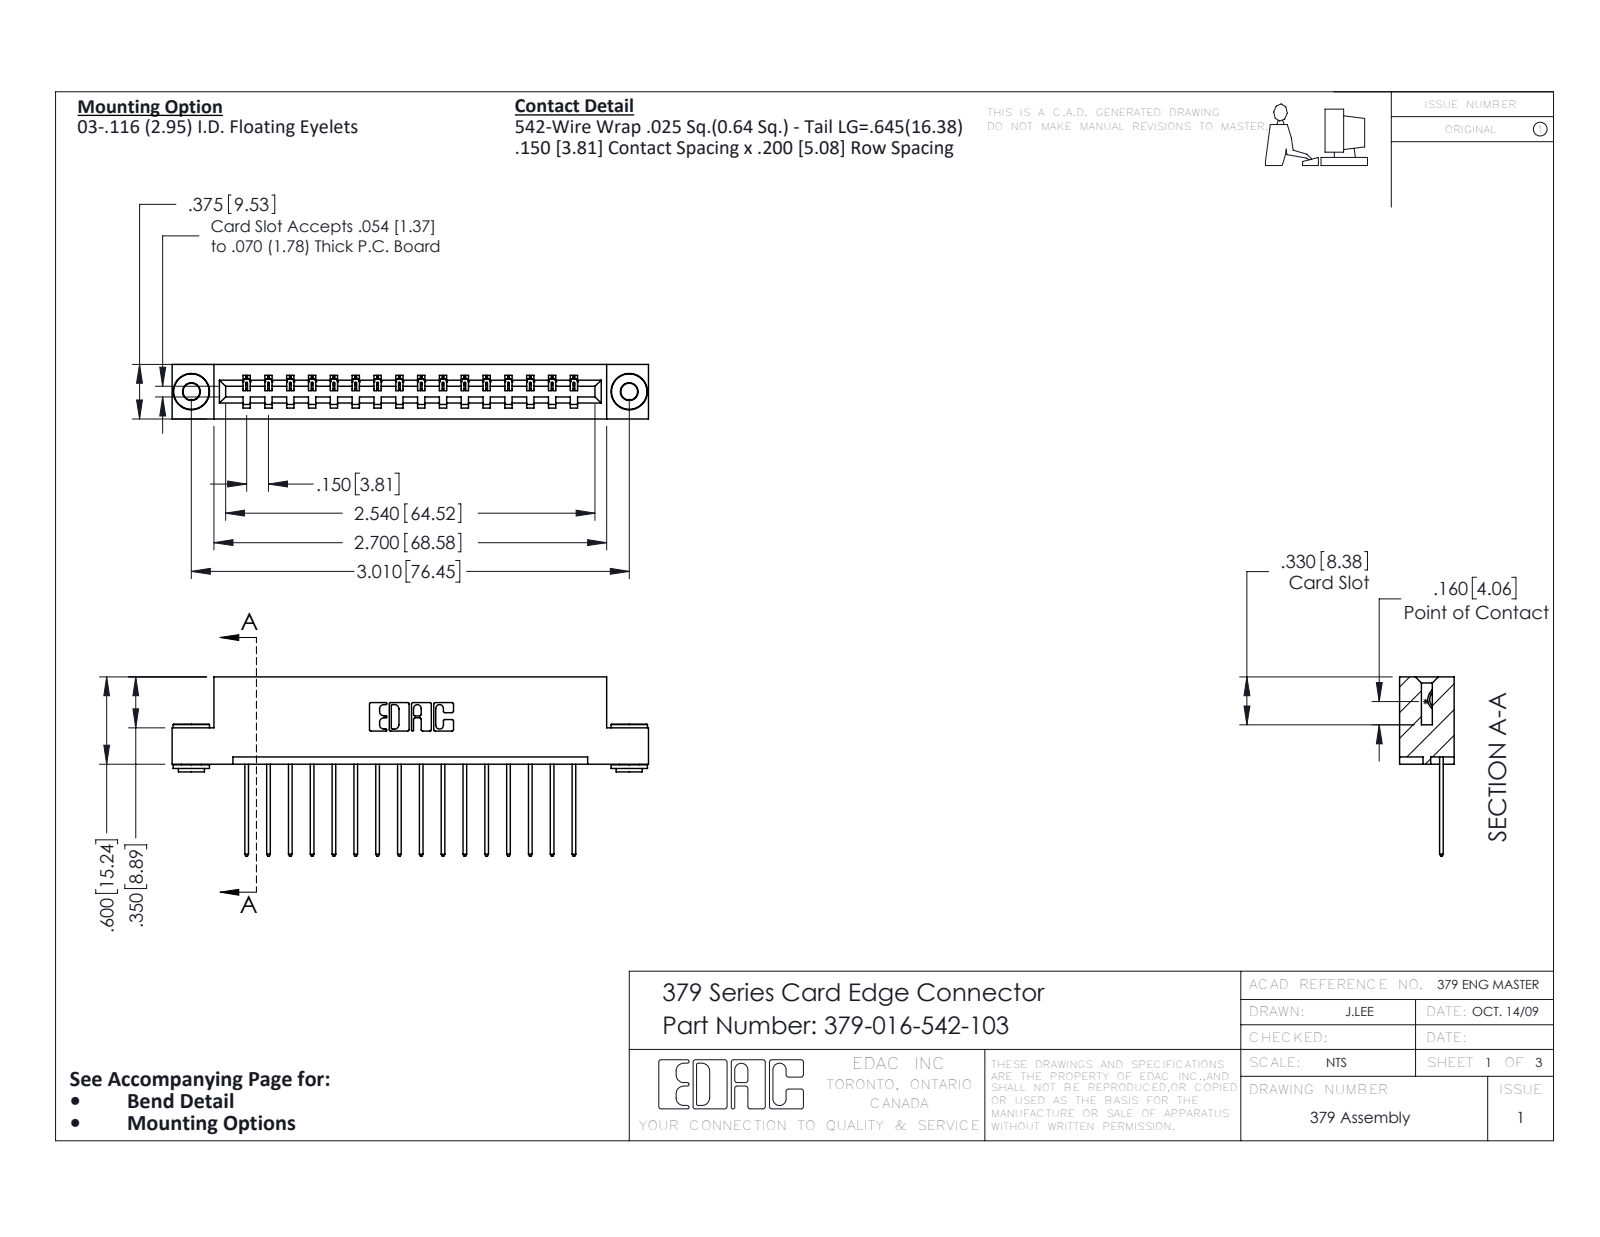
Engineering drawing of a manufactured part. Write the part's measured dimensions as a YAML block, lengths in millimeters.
part_name: "379 Part_Flush - .156 Dia - TH; 345-292-001_345-293-142; 379-016-542-103; 345-250-002_345-250-002-102"
step_written_by: "SolidWorks 2020 (CONFIG_CONTROL_DESIGN)"
units: millimeters
bodies: {solids: 19, faces: 1080, planar: 752, cylindrical: 320, other: 8}
overall_size: [83.2, 31.3, 9.5]
volume: 8490
surface_area: 9019
round_holes:
  - {diameter: 2.9, count: 2}
  - {diameter: 4, count: 2}
round_bosses_or_shafts:
  - {diameter: 6.4, count: 2}
  - {diameter: 4.6, count: 2}
  - {diameter: 3.5, count: 2}
partial_cylinders:
  - {radius: 0.2, count: 32}
  - {radius: 0.3, count: 32}
  - {radius: 0.3, count: 22}
  - {radius: 0.2, count: 6}
  - {radius: 0.8, count: 6}
  - {radius: 0.7, count: 3}
  - {radius: 0.4, count: 1}
  - {radius: 0.6, count: 1}
face_to_face_distances: [7.6, 1.9, 9.5, 15.2, 3.8, 5.7, 5.1, 7, 11.4, 0.6]
hole_center_spacings: [76.5]
